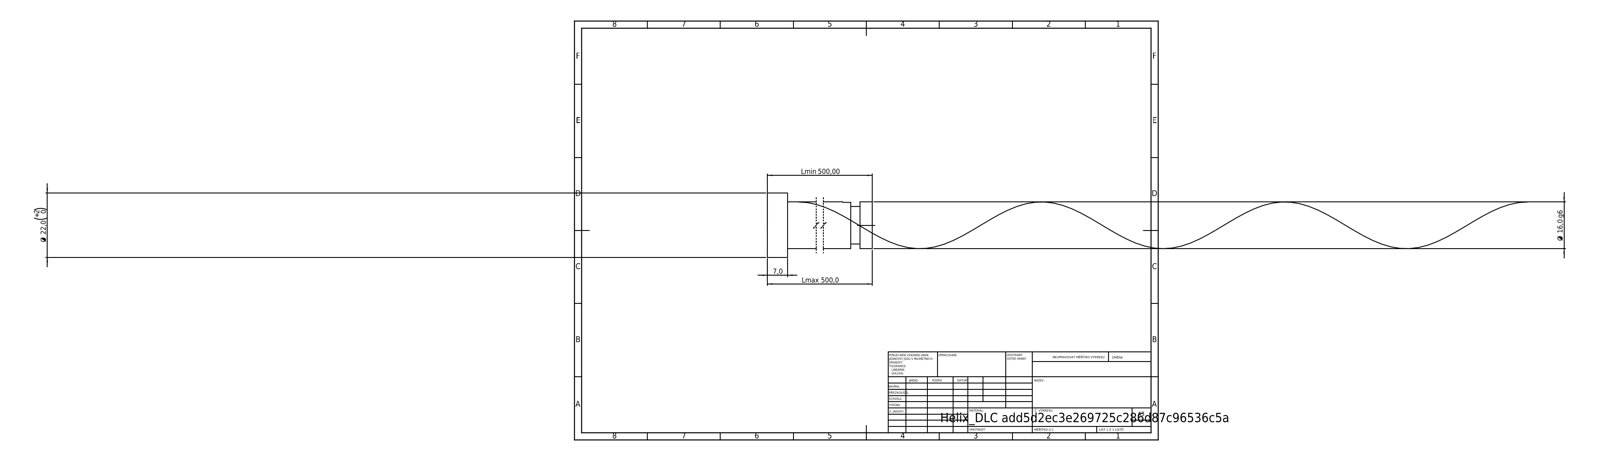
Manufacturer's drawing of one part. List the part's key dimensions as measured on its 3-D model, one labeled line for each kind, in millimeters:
STEP written by: SolidWorks 2019 (CONFIG_CONTROL_DESIGN)
Units: millimetres
Bodies: 1 solid, 21 faces (6 planar, 14 cylindrical, 1 other)
Overall size (bounding box): 500 × 22 × 22
Volume: 100 590 mm³ · Surface area: 26 607 mm²
Round bosses / shafts (diameter × count): ⌀22 ×1, ⌀16 ×1, ⌀12.8 ×1
Main face-to-face distances: 500, 7, 493, 495.8, 488.8, 4.2, 492.6, 485.6, 3.2, 7.4
